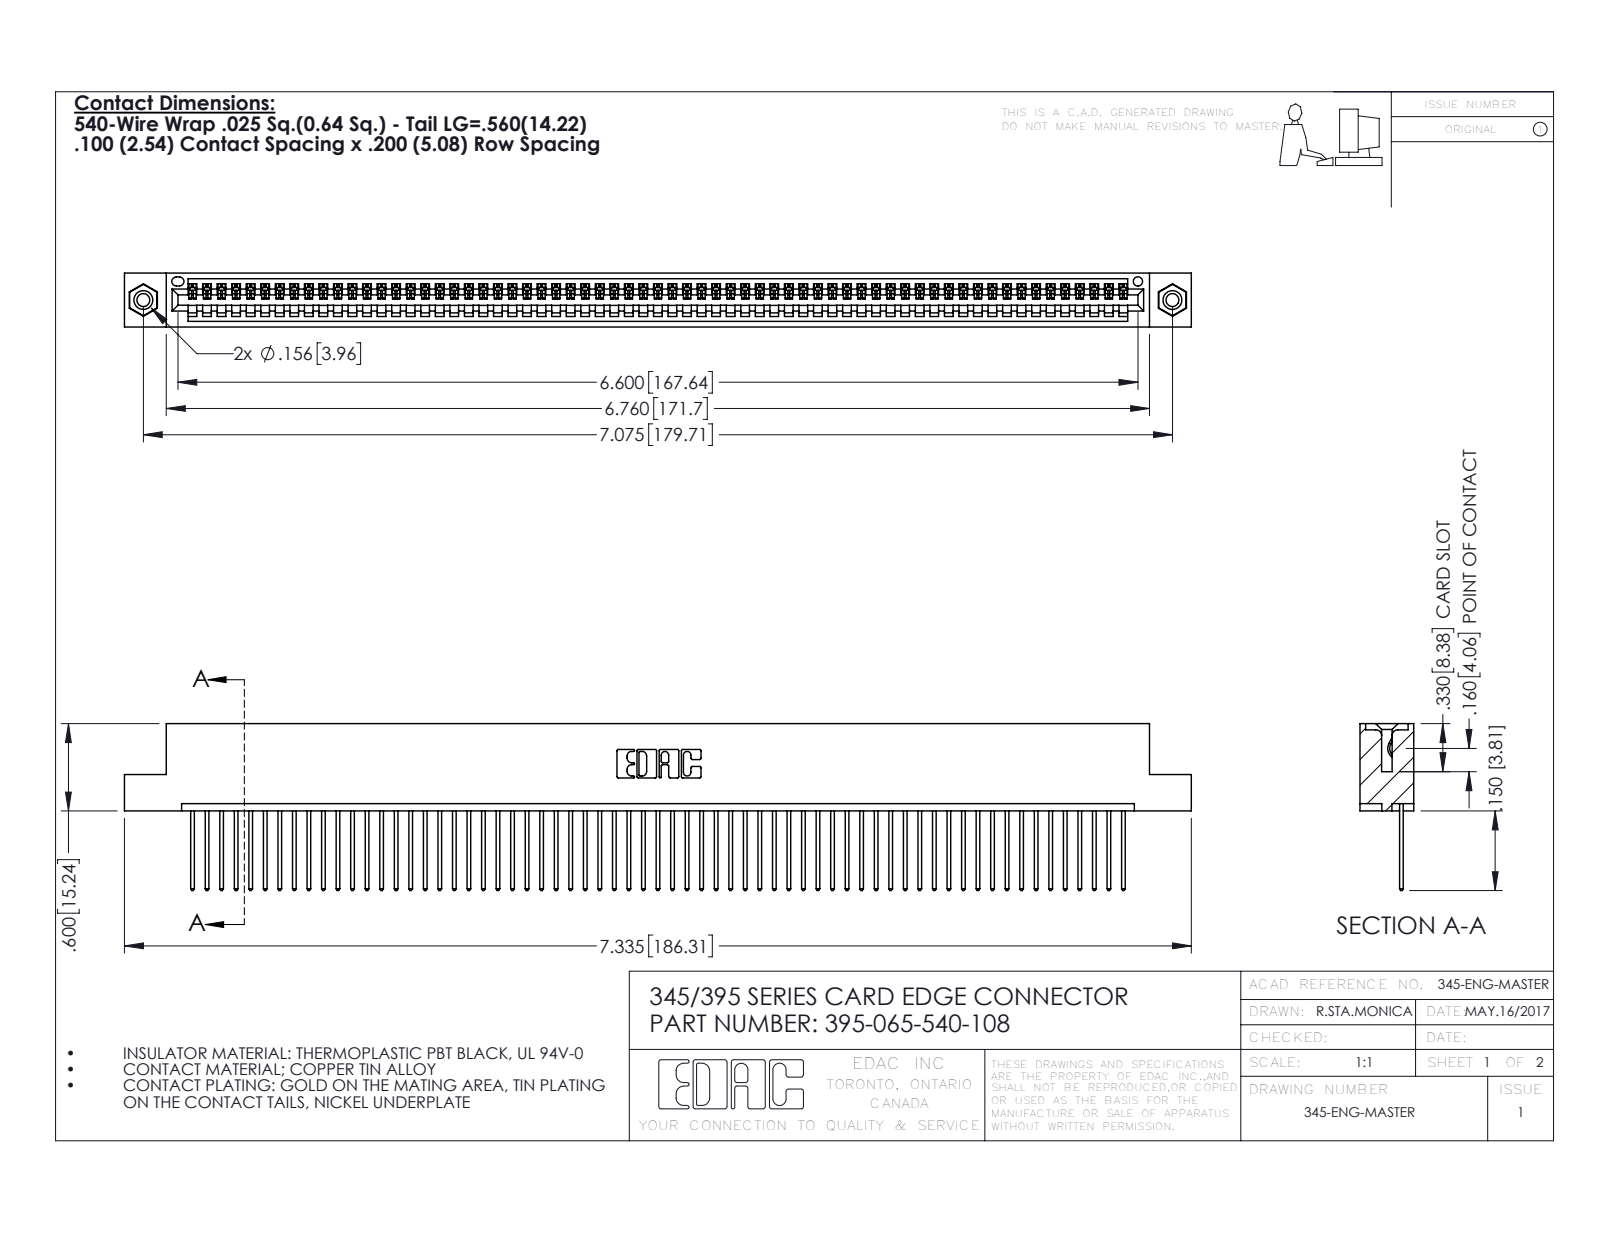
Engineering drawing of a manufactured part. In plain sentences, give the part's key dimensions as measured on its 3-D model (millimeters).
The part is named "395-065-540-108; 345 Part_Flush Mounting Lugs - 0.156 Dia-TI; 345-292-001_345-293-140; 345-250-001_345-250-003-102". Its 3-D file was written by "SolidWorks 2016 (CONFIG_CONTROL_DESIGN)". It is 68 solids with 3956 faces: 2712 planar, 1228 cylindrical and 16 other. Overall it measures 186.3 by 29.1 by 9.4 millimeters. Its volume is 17 960 cubic millimeters and its surface area 24 840 square millimeters. Round holes: 2 of diameter 2.3, 2 of diameter 3.2, 2 of diameter 4, 1 of diameter 1.6. Round bosses or shafts: 2 of diameter 3.9. Partial cylindrical surfaces (rounded edges, fillets, slot ends): 130 of radius 0.2, 130 of radius 0.3, 22 of radius 0.3, 6 of radius 0.2, 6 of radius 0.8, 3 of radius 0.7, 2 of radius 0.8, 2 of radius 1. The main face-to-face distances are 1.8, 7.6, 9.4, 2.5, 6.9, 0.6, 5.1, 5.7, 3.8, 1.8. The hole center spacings are 6.9, 173.7, 179.7.
